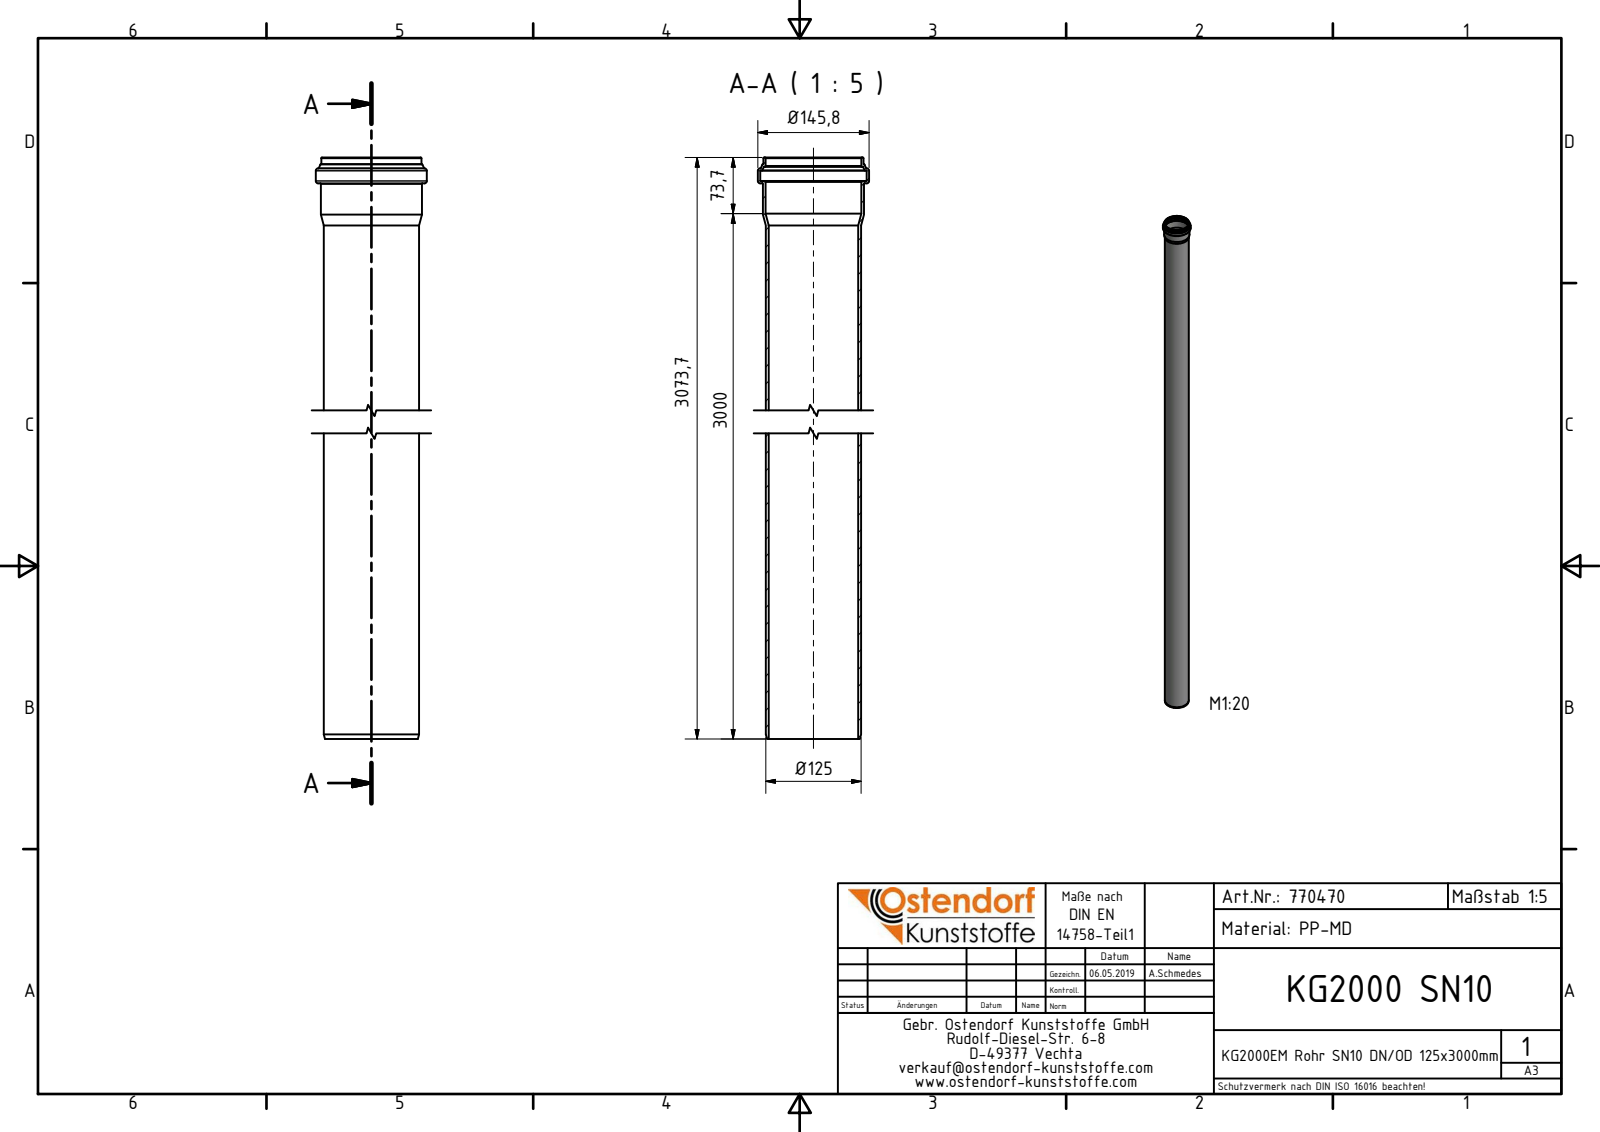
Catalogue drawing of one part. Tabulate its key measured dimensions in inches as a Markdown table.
| quantity | value |
| --- | --- |
| part name | 770470 KG2000EM Rohr SN10 DN-OD125x3000 |
| STEP written by | Autodesk Inventor 2016 (AUTOMOTIVE_DESIGN) |
| units | inches |
| bodies | 1 solid, 35 faces (5 planar, 8 cylindrical, 22 other) |
| overall size | 121.012 × 5.74 × 5.74 |
| volume | 278.6 in³ |
| surface area | 3 650 in² |
| round holes (diameter × count) | 4.614 × 1, 4.941 × 1, 5.504 × 1 |
| round bosses / shafts (diameter × count) | 5.74 × 1, 5.224 × 1, 5.177 × 1, 4.921 × 1 |
| main face-to-face distances | 119.685, 121.012, 1.327, 120.664, 0.979, 0.348, 120.453, 0.768, 0.211, 0.559 |
